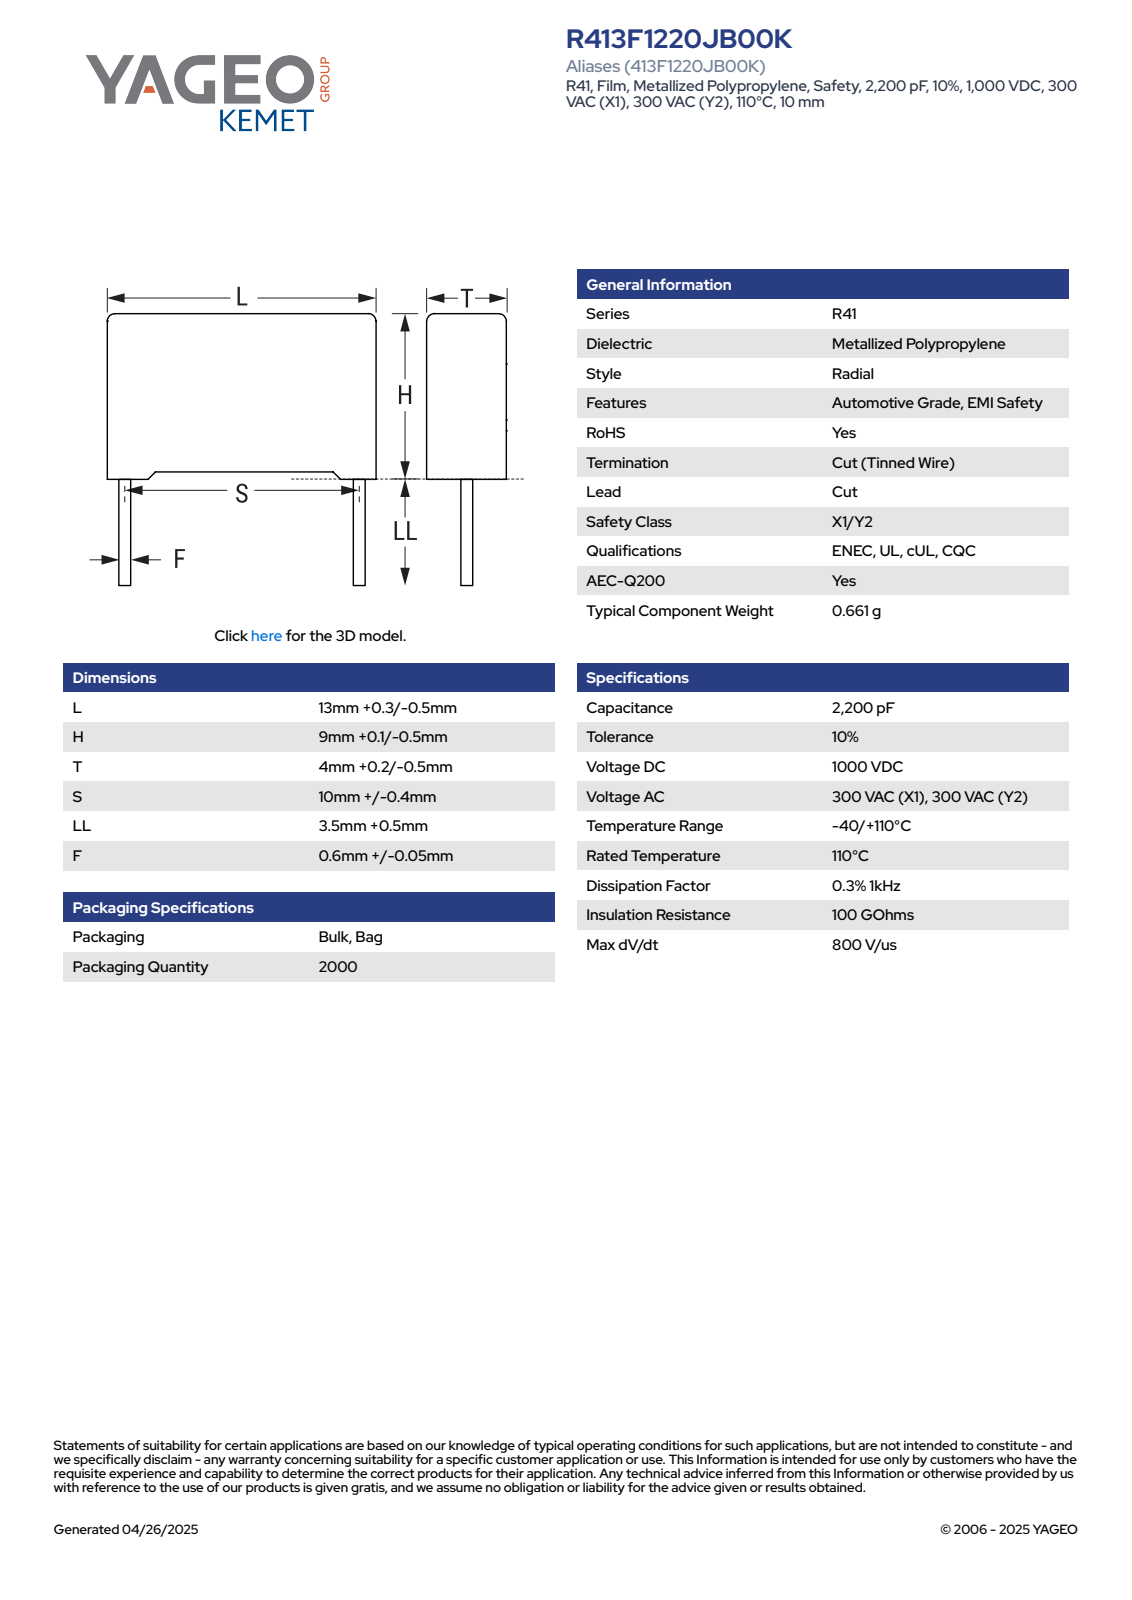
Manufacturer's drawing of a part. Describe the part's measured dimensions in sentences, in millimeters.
The part is named "CFR_RB2_13X9X4_L13.3H9.1T4.2S10LL4F0.65". Its 3-D file was written by "SolidWorks 2021 (AUTOMOTIVE_DESIGN)". It is 4 solids with 85 faces: 77 planar, 8 cylindrical and 0 other. Overall it measures 13.3 by 13.1 by 4.21 millimeters. Its volume is 477 cubic millimeters and its surface area 471 square millimeters. Round bosses or shafts: 2 of diameter 0.65. Partial cylindrical surfaces (rounded edges, fillets, slot ends): 4 of radius 0.5. The main face-to-face distances are 4.2, 8.35, 13.3, 0.44, 3.76, 0.75, 9.1, 3.32, 0.31, 8.79.
